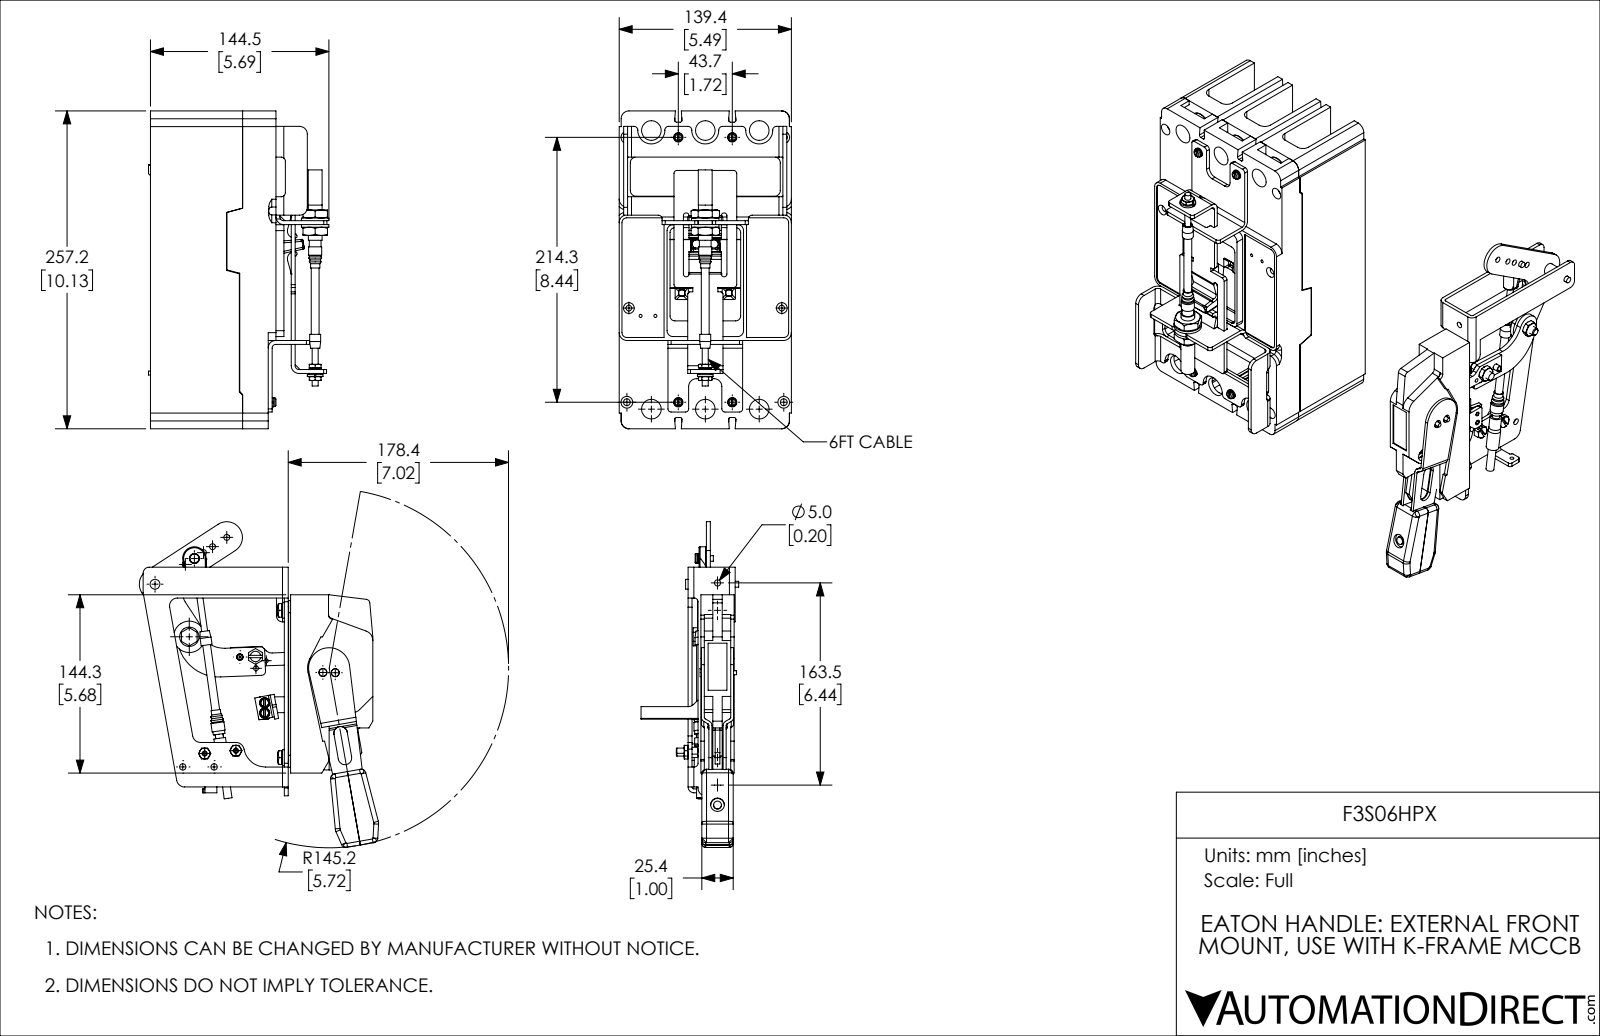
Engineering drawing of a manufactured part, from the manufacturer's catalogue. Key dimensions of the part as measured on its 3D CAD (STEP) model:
Part name (STEP PRODUCT): F3S06HPX_BREAKER; F3S06HPX_HANDLE; F3S06HPX
STEP written by: SolidWorks 2019 (CONFIG_CONTROL_DESIGN)
Units: inches
Bodies: 81 solids, 2972 faces (1428 planar, 1143 cylindrical, 401 other)
Overall size (bounding box): 14.165 × 10.378 × 7.627
Volume: 182.3 in³ · Surface area: 888.8 in²
Round holes (diameter × count): ⌀0.219 ×8, ⌀0.203 ×6, ⌀0.228 ×6, ⌀0.625 ×6, ⌀0.188 ×5, ⌀0.196 ×5, ⌀0.281 ×5, ⌀0.375 ×5, ⌀0.438 ×5, ⌀0.168 ×4, ⌀0.25 ×4, ⌀0.5 ×4
Round bosses / shafts (diameter × count): ⌀0.25 ×9, ⌀0.338 ×6, ⌀0.375 ×5, ⌀0.5 ×4, ⌀0.297 ×4, ⌀0.27 ×4, ⌀0.138 ×4, ⌀0.394 ×3
Partial cylindrical surfaces — rounded edges, fillets, slot ends (radius × count): R0.062 ×109, R0.125 ×53, R0.25 ×50, R0.032 ×22, R0.156 ×18, R0.1 ×16, R0.188 ×16, R0.031 ×15
Main face-to-face distances: 0.125, 5.49, 0.249, 2.906, 1.062, 3.719, 0.813, 0.032, 4, 0.156
Hole centre spacings: 1.719, 8.17, 7.907, 8.7, 9.04, 0.531, 1.141, 1.141
